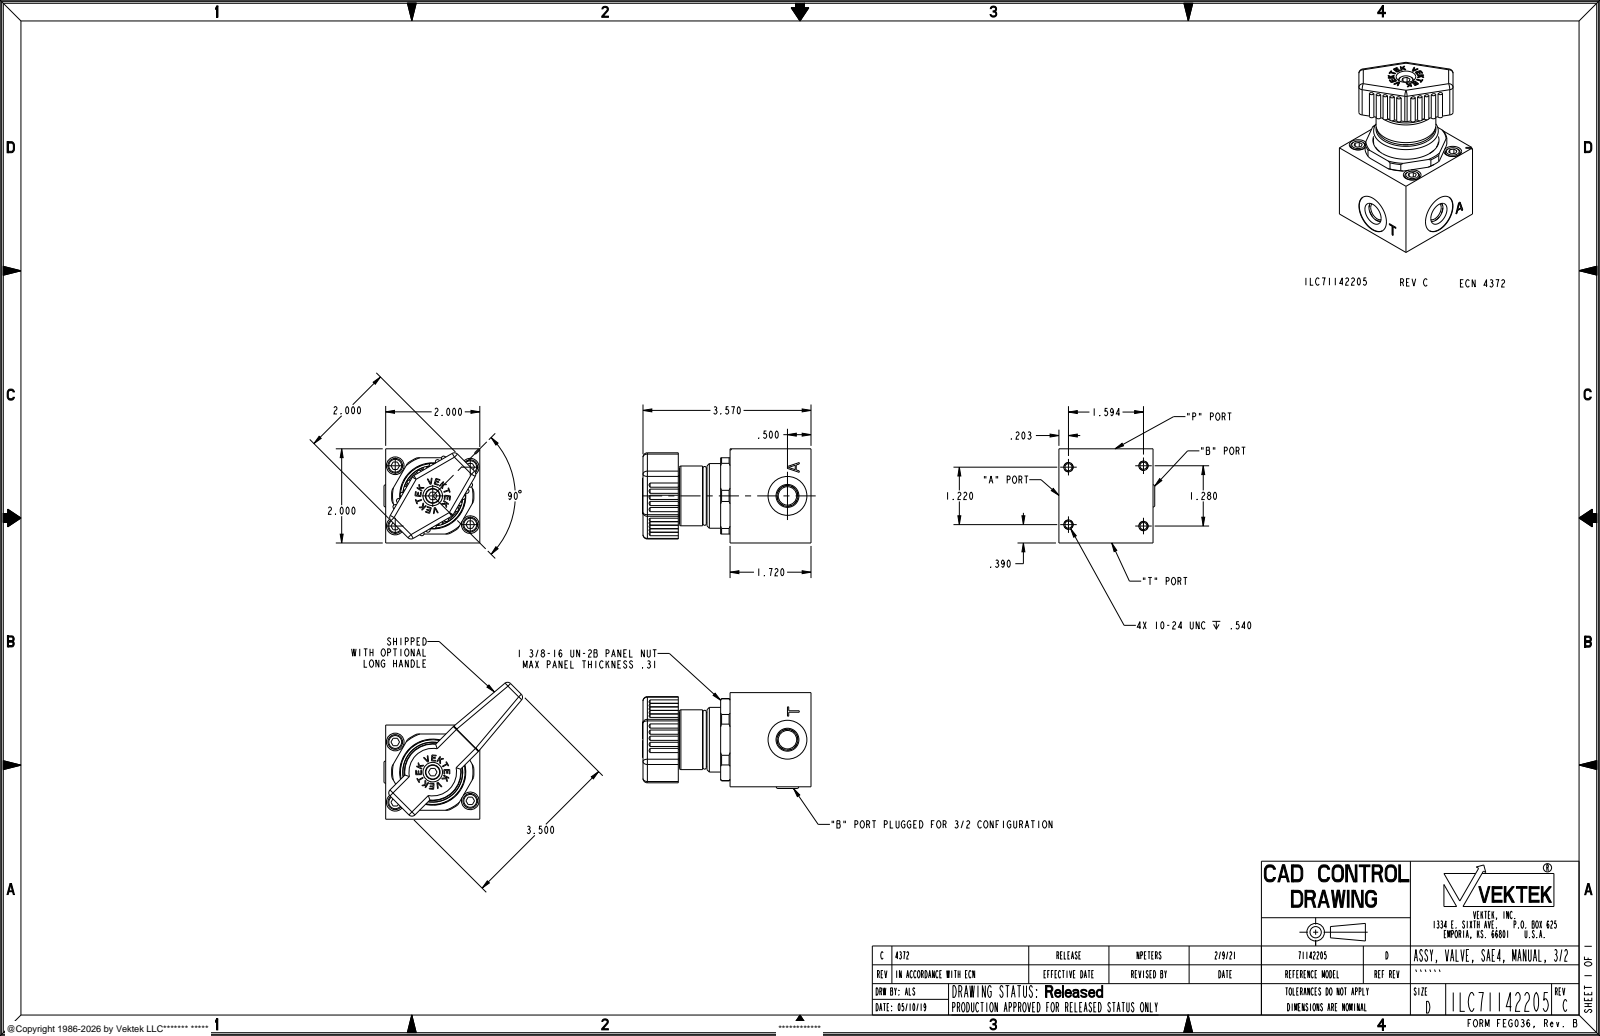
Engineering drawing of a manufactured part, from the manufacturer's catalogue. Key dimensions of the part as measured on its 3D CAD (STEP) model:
Part name (STEP PRODUCT): ILC71142205_BODY; ILC71142205_ADAPTER; 85600903; 87114013 (+2 more)
STEP written by: PRO/ENGINEER BY PARAMETRIC TECHNOLOGY CORPORATION, 2013320 (AP203_CONFIGURATION_CONTROLLED_3D_DESIGN_OF_MECHANICAL_PARTS_AND_ASSEMBLIES_MIM_LF)
Units: inches
Bodies: 6 solids, 1741 faces (1405 planar, 216 cylindrical, 120 other)
Overall size (bounding box): 3.58 × 2.944 × 2.908
Volume: 10.16 in³ · Surface area: 75.58 in²
Round holes (diameter × count): ⌀0.151 ×4, ⌀0.196 ×4, ⌀0.375 ×4, ⌀0.199 ×2, ⌀0.392 ×2, ⌀0.825 ×2, ⌀0.203 ×1, ⌀0.204 ×1, ⌀0.205 ×1, ⌀0.415 ×1, ⌀0.5 ×1, ⌀1.314 ×1
Round bosses / shafts (diameter × count): ⌀0.19 ×5, ⌀0.313 ×4, ⌀0.437 ×2, ⌀1.387 ×1, ⌀1.373 ×1, ⌀1.27 ×1, ⌀0.312 ×1
Partial cylindrical surfaces — rounded edges, fillets, slot ends (radius × count): R0.09 ×23, R0.048 ×20, R0.093 ×12, R0.03 ×10, R0.045 ×8, R0.062 ×8, R0.031 ×6, R0.12 ×4
Main face-to-face distances: 2, 1.72, 0.32, 1.1, 2.82, 0.1, 0.75, 1.42, 3.14, 0.53
Hole centre spacings: 0.437, 1.004, 1.022, 1.594, 2.026, 0.573, 0.589, 0.874
